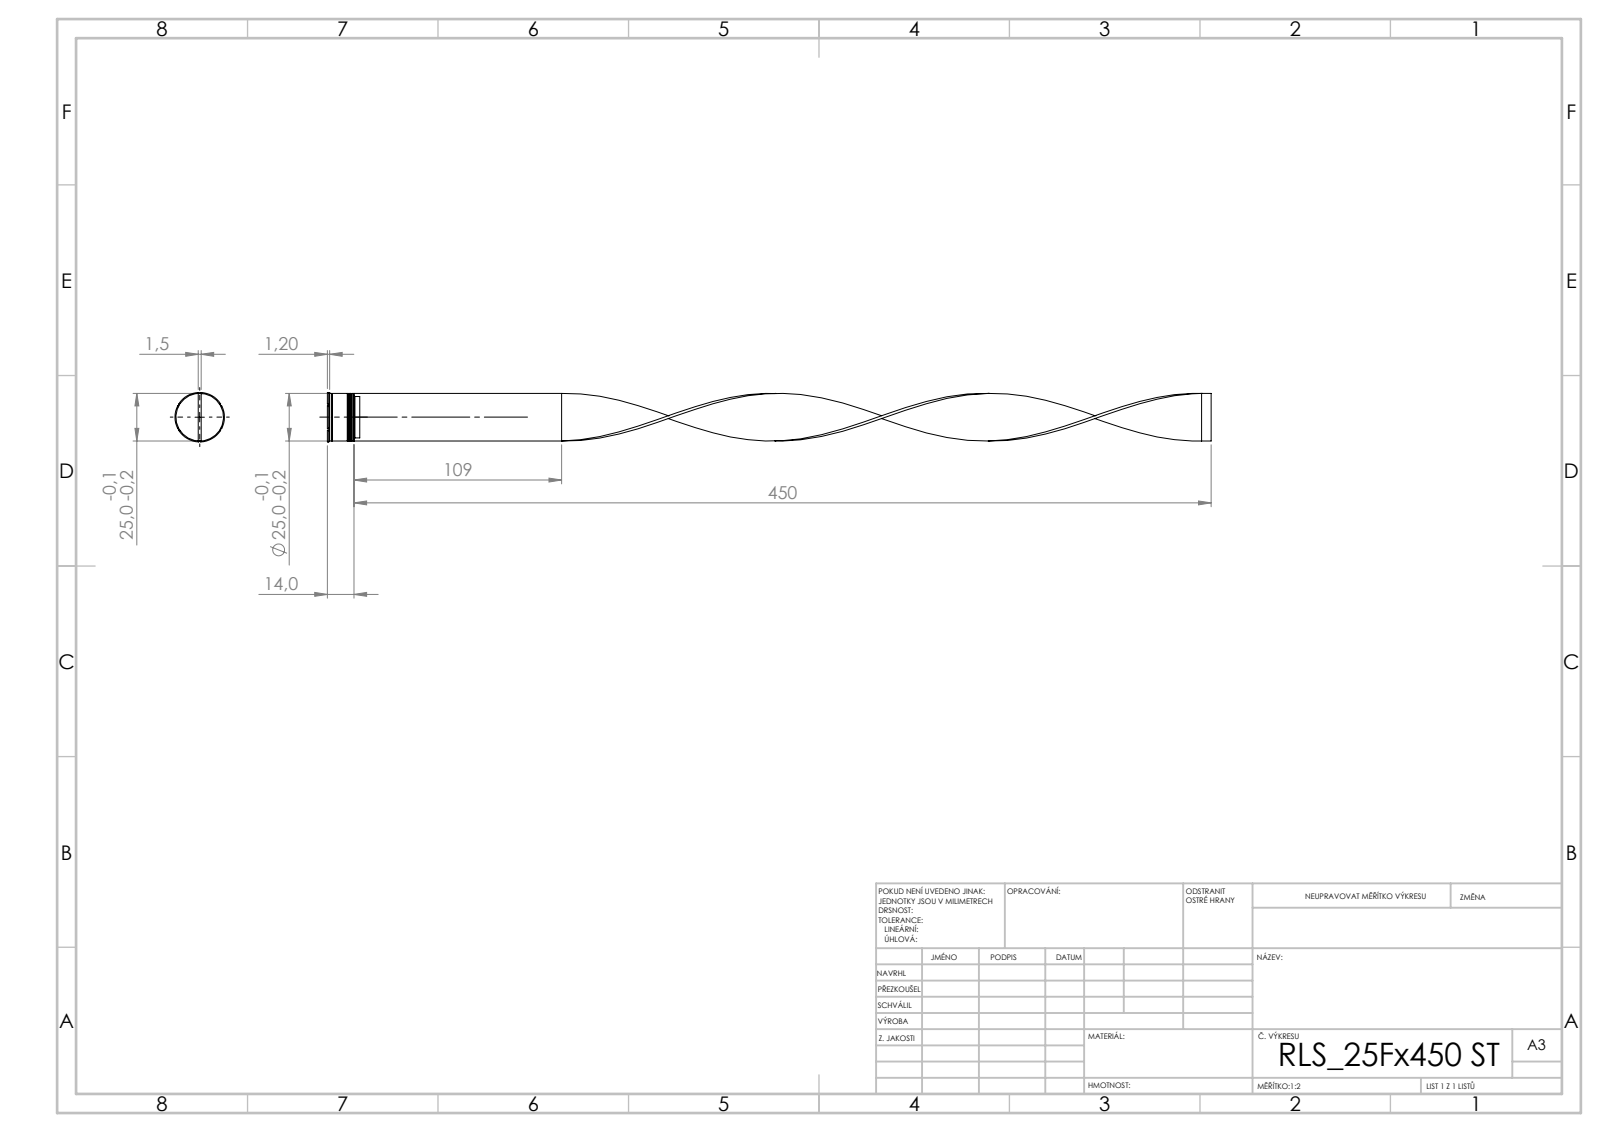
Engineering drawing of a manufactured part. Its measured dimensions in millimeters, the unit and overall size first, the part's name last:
Units: millimetres
Overall size (bounding box): 464 × 26 × 25.98
Round bosses / shafts (diameter × count): ⌀26 ×1, ⌀25 ×1, ⌀24.4 ×1, ⌀21.8 ×1
Partial cylindrical surfaces — rounded edges, fillets, slot ends (radius × count): R11 ×1
Main face-to-face distances: 1.5, 0.7, 2.2, 0.8, 11.7, 11, 10.2, 9.5, 4.3, 5
Volume: 25 001 mm³ · Surface area: 28 633 mm²
Bodies: 3 solids, 108 faces (48 planar, 33 cylindrical, 27 other)
STEP written by: SolidWorks 2019 (CONFIG_CONTROL_DESIGN)
